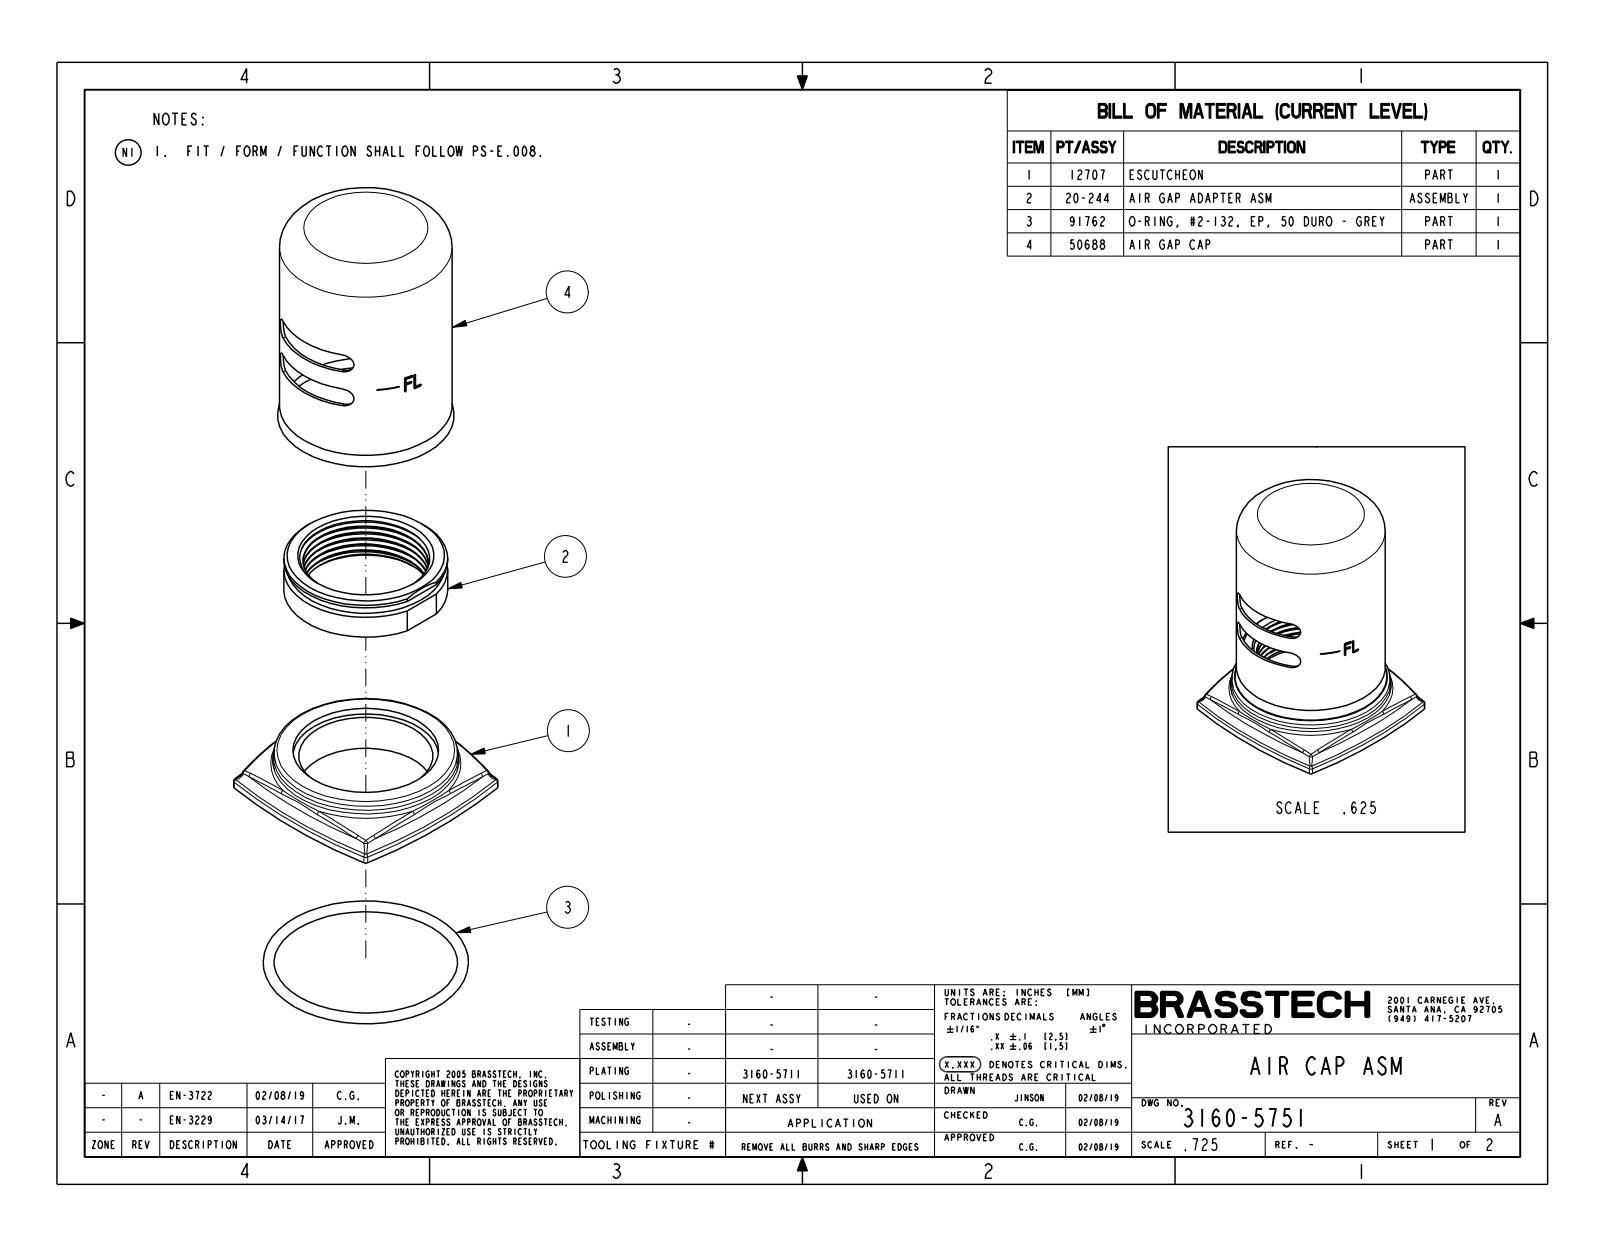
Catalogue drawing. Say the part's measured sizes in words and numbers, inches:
The part is named "12707; 12736; 91227; 20-244_ASM (+3 more)". Its 3-D file was written by "CREO PARAMETRIC BY PTC INC, 2018400 (CONFIG_CONTROL_DESIGN)". It is 5 solids with 276 faces: 42 planar, 76 cylindrical and 158 other. Overall it measures 2.616 by 1.943 by 1.943 inches. Its volume is 1.312 cubic inches and its surface area 64.71 square inches. Round holes: 1 of diameter 1.19, 1 of diameter 1.27, 1 of diameter 1.38, 1 of diameter 1.575. Round bosses or shafts: 1 of diameter 1.635, 1 of diameter 1.55, 1 of diameter 1.39, 1 of diameter 1.36. Partial cylindrical surfaces (rounded edges, fillets, slot ends): 4 of radius 0.03, 4 of radius 0.083, 4 of radius 0.098, 4 of radius 0.203, 4 of radius 5.03, 4 of radius 5.15, 4 of radius 5.18, 4 of radius 5.25. The main face-to-face distances are 2.19, 0.425, 2.615, 2.585, 2.16, 0.03, 0.825, 0.4, 1.76, 1.79.
